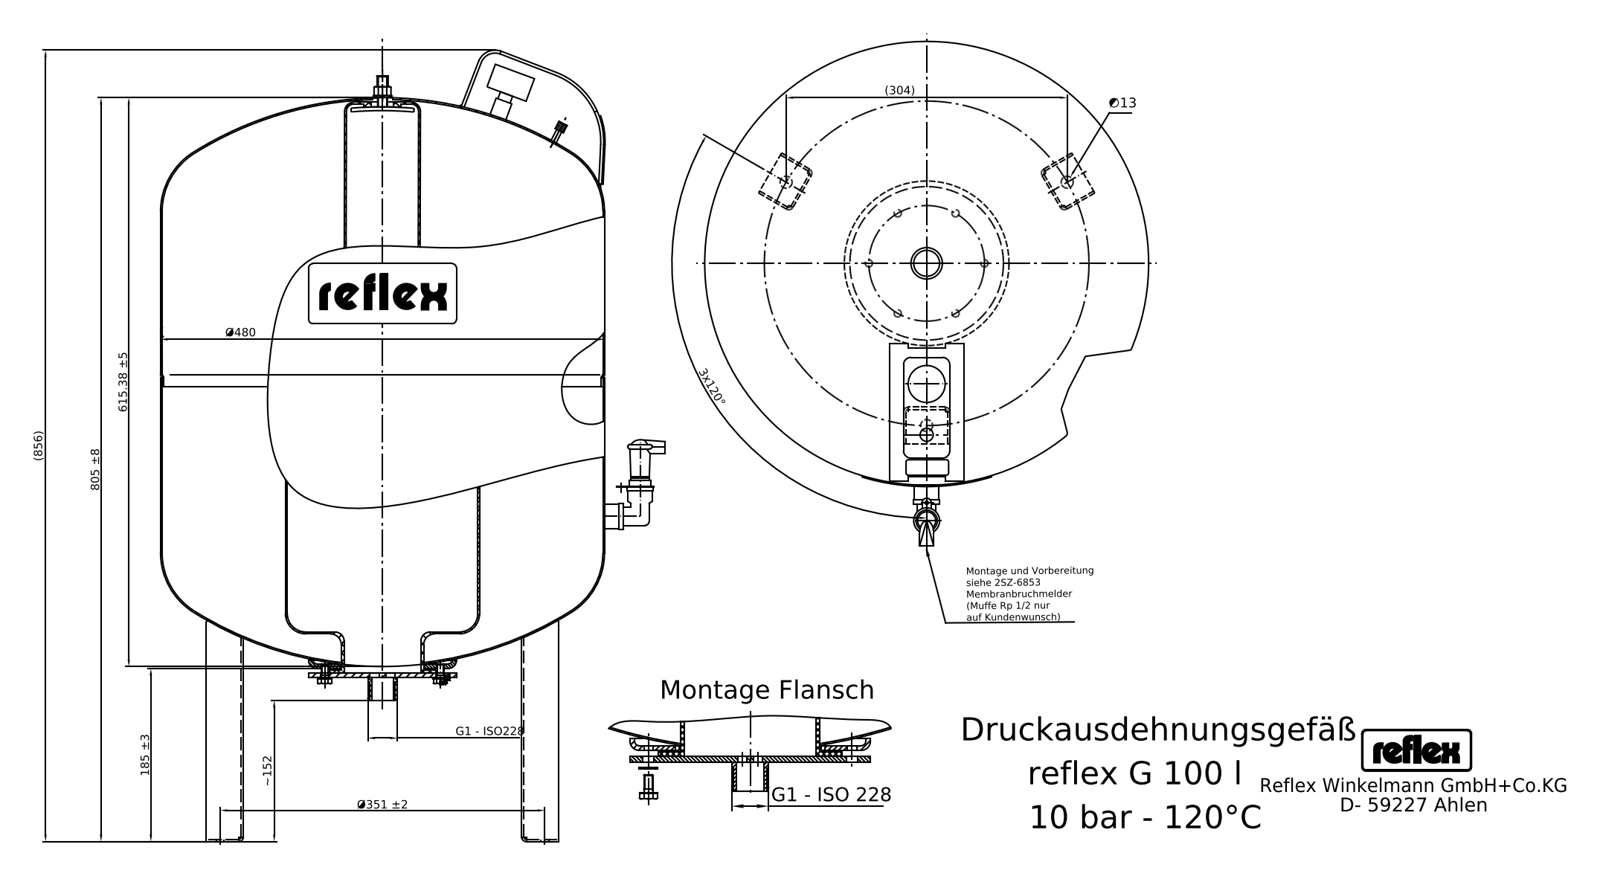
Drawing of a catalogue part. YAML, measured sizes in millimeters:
step_written_by: "Mechanical Desktop 2008 (CONFIG_CONTROL_DESIGN)"
units: millimeters
bodies: {solids: 21, faces: 499, planar: 215, cylindrical: 184, other: 100}
overall_size: [851.24, 545, 481.14]
volume: 95140000
surface_area: 2152000
round_holes:
  - {diameter: 13.4, count: 3}
  - {diameter: 2.48, count: 1}
  - {diameter: 3.8, count: 1}
  - {diameter: 4.3, count: 1}
  - {diameter: 4.4, count: 1}
  - {diameter: 5.45, count: 1}
  - {diameter: 7, count: 1}
  - {diameter: 8, count: 1}
  - {diameter: 10, count: 1}
  - {diameter: 11.4, count: 1}
  - {diameter: 89, count: 1}
  - {diameter: 150, count: 1}
round_bosses_or_shafts:
  - {diameter: 8, count: 6}
  - {diameter: 28, count: 2}
  - {diameter: 26, count: 2}
  - {diameter: 20, count: 2}
  - {diameter: 480, count: 1}
  - {diameter: 160, count: 1}
  - {diameter: 140, count: 1}
  - {diameter: 62, count: 1}
partial_cylinders:
  - {radius: 1, count: 15}
  - {radius: 2.5, count: 15}
  - {radius: 5, count: 15}
  - {radius: 3.94, count: 4}
  - {radius: 1.57, count: 3}
  - {radius: 2.69, count: 2}
  - {radius: 4.72, count: 2}
  - {radius: 6.49, count: 2}
face_to_face_distances: [345, 2.5, 47.5, 5, 50, 45, 143, 488, 148, 493]
hole_center_spacings: [175.5, 303.98, 226.36, 255.5, 431]
